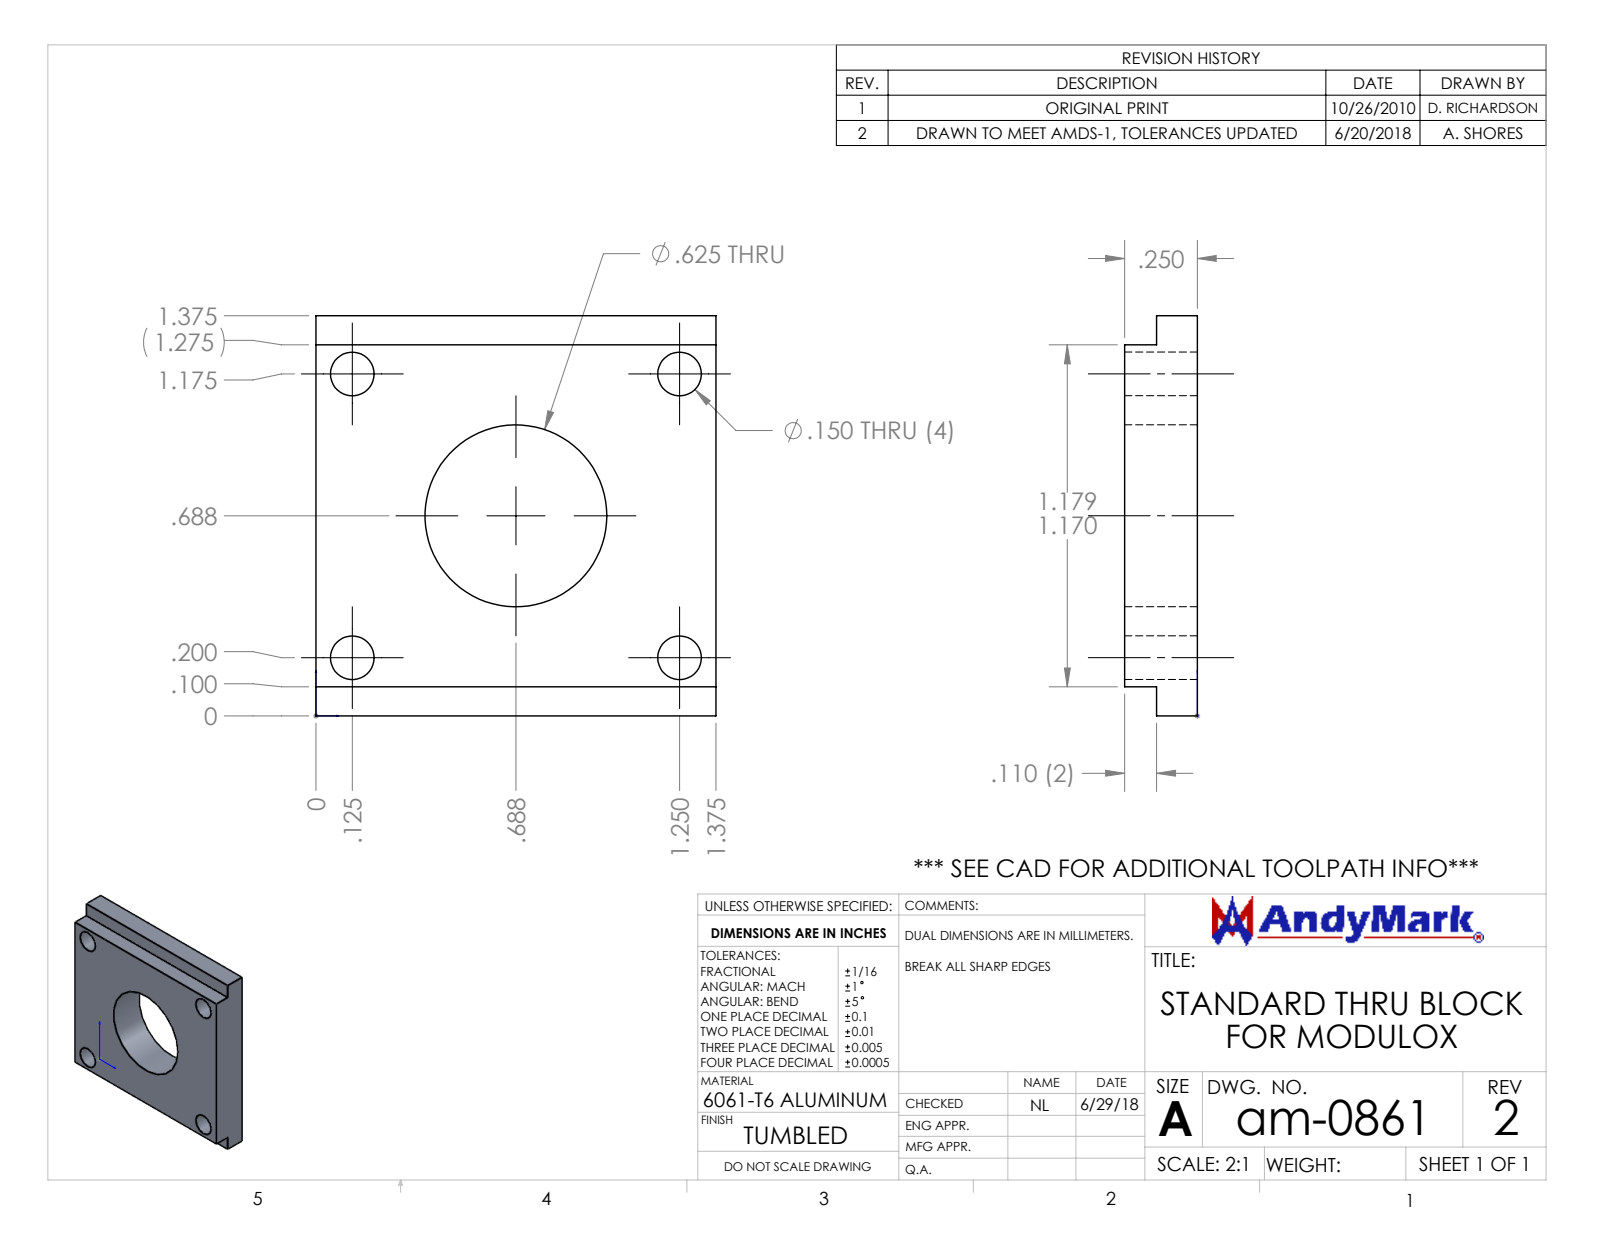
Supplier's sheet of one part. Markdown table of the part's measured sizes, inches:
| quantity | value |
| --- | --- |
| part name | am-0861 Thru Block for Modulox REV2 |
| STEP written by | SolidWorks 2017 (AUTOMOTIVE_DESIGN) |
| units | inches |
| bodies | 1 solid, 20 faces (10 planar, 10 cylindrical, 0 other) |
| overall size | 1.375 × 1.375 × 0.25 |
| volume | 0.348 in³ |
| surface area | 5.319 in² |
| round holes (diameter × count) | 0.15 × 4, 0.625 × 1 |
| main face-to-face distances | 0.25, 1.375, 0.1, 1.275, 0.14, 0.11, 1.175 |
| hole center spacings | 0.744, 0.975, 1.125, 1.489 |
